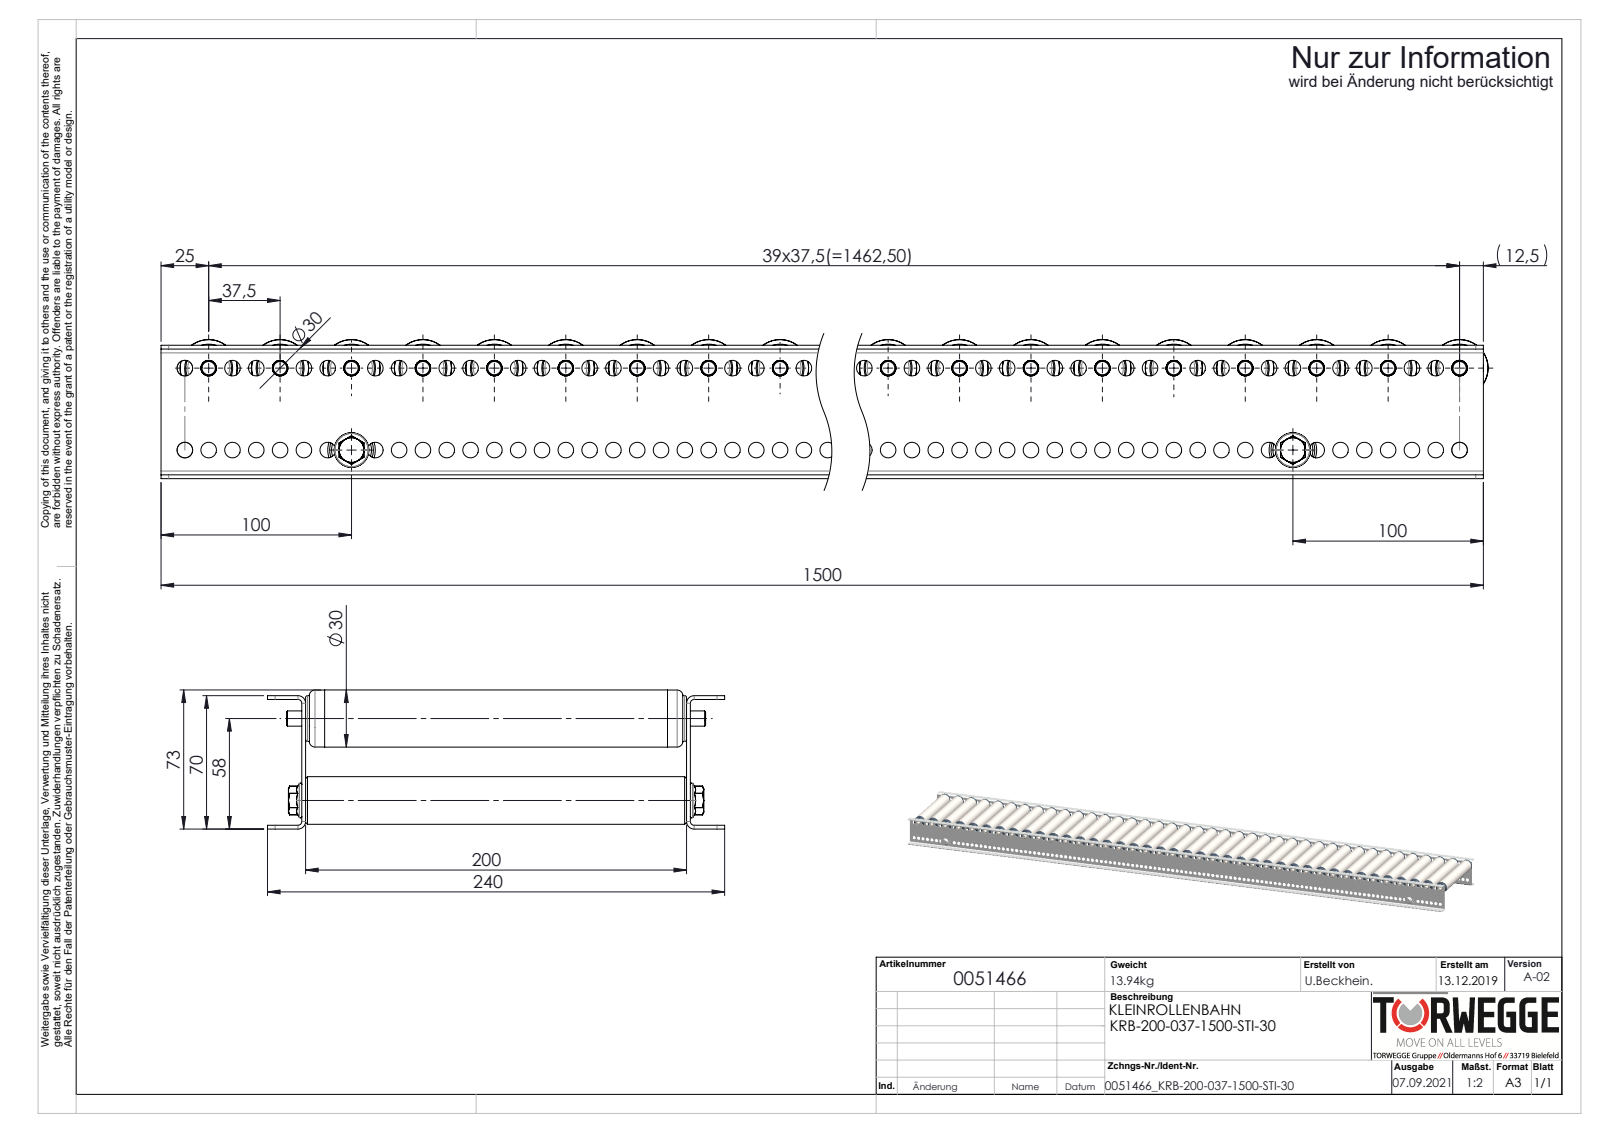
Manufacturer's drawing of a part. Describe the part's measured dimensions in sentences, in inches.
The part is named "0040250_DRUCK-FEDER-8mm; KUT50-30x1,5-STI-A8-FA_KFG_S100903_KUT50-30x1,5-STI-A8-FA-EL=200; 0042503_Typ-KUT50-30x1,5-A8; 0039768_Tragrollenrohr-Ø30x1,5STI_KFG_0039768_L=180 (+6 more)". Its 3-D file was written by "SolidWorks 2020 (AUTOMOTIVE_DESIGN)". It is 252 solids with 10592 faces: 3320 planar, 4208 cylindrical and 3064 other. Overall it measures 59.154 by 9.449 by 2.874 inches. Its volume is 127.5 cubic inches and its surface area 4 287 square inches. Round holes: 238 of diameter 0.323, 40 of diameter 0.315, 40 of diameter 0.319, 40 of diameter 0.913, 40 of diameter 0.992, 40 of diameter 1.063, 2 of diameter 0.268, 2 of diameter 0.827. Round bosses or shafts: 40 of diameter 1.181, 40 of diameter 1.177, 40 of diameter 1.067, 40 of diameter 1.055, 40 of diameter 0.945, 40 of diameter 0.551, 2 of diameter 0.984, 2 of diameter 0.315. Partial cylindrical surfaces (rounded edges, fillets, slot ends): 40 of radius 0.199, 8 of radius 0.157, 4 of radius 0.079. The main face-to-face distances are 0.079, 7.953, 7.874, 2.677, 8.031, 2.756, 2.598, 0.394, 7.48, 0.787. The hole center spacings are 0.492, 0.984, 1.476, 1.969, 2.461, 2.953, 3.445, 3.937.
